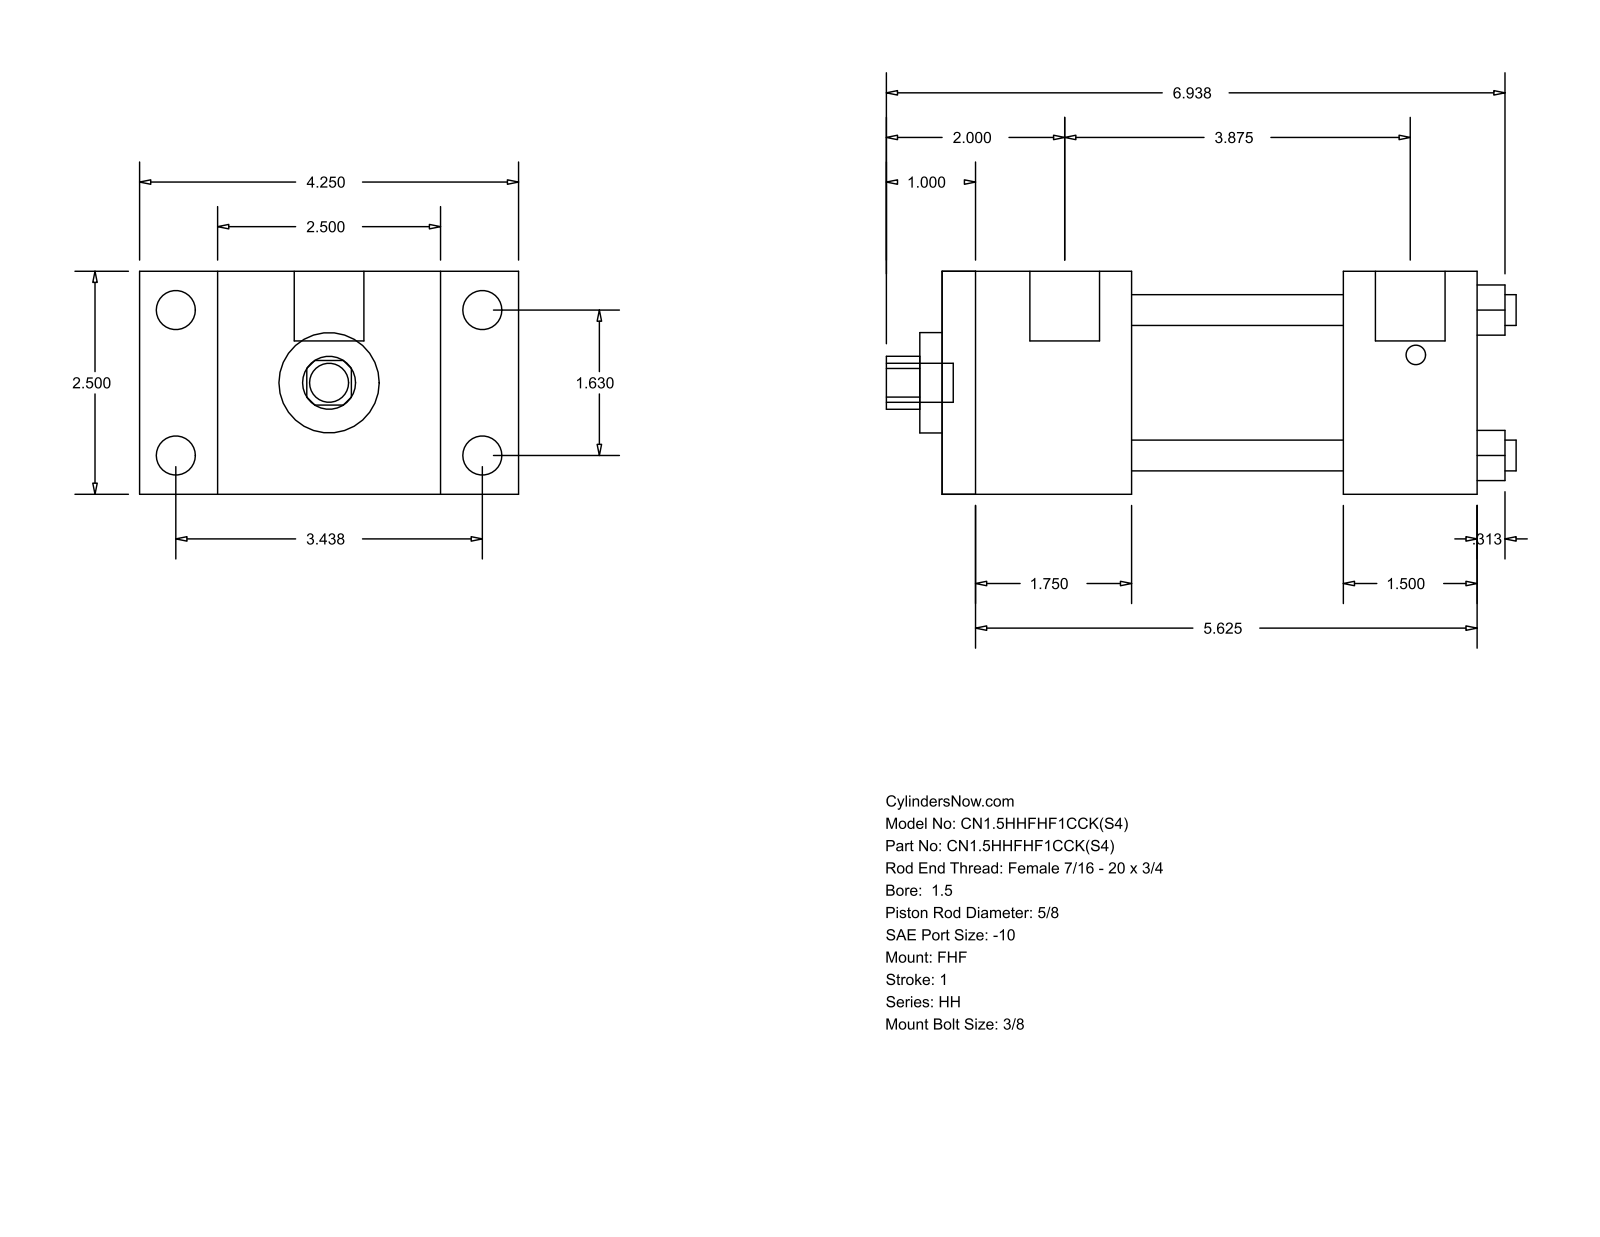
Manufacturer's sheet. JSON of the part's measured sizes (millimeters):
{"part_name": "HH_FHF__0150_0.625", "step_written_by": "GSSL Pune (CONFIG_CONTROL_DESIGN)", "units": "millimeters", "bodies": {"solids": 0, "faces": 88, "planar": 60, "cylindrical": 28, "other": 0}, "overall_size": [179.39, 107.95, 63.5], "round_holes": [[8.76, 4], [15.88, 1], [28.57, 1], [44.45, 1]], "round_bosses_or_shafts": [[11.13, 4], [5.56, 4], [19.84, 2], [11.11, 1]], "partial_cylinders_radius": [[7.54, 1]], "face_to_face_distances": [63.5, 22.23, 85.73, 53.97, 107.96, 152.4, 98.43, 38.1, 60.33, 114.3], "hole_center_spacings": [29.27, 41.4, 58.55]}
